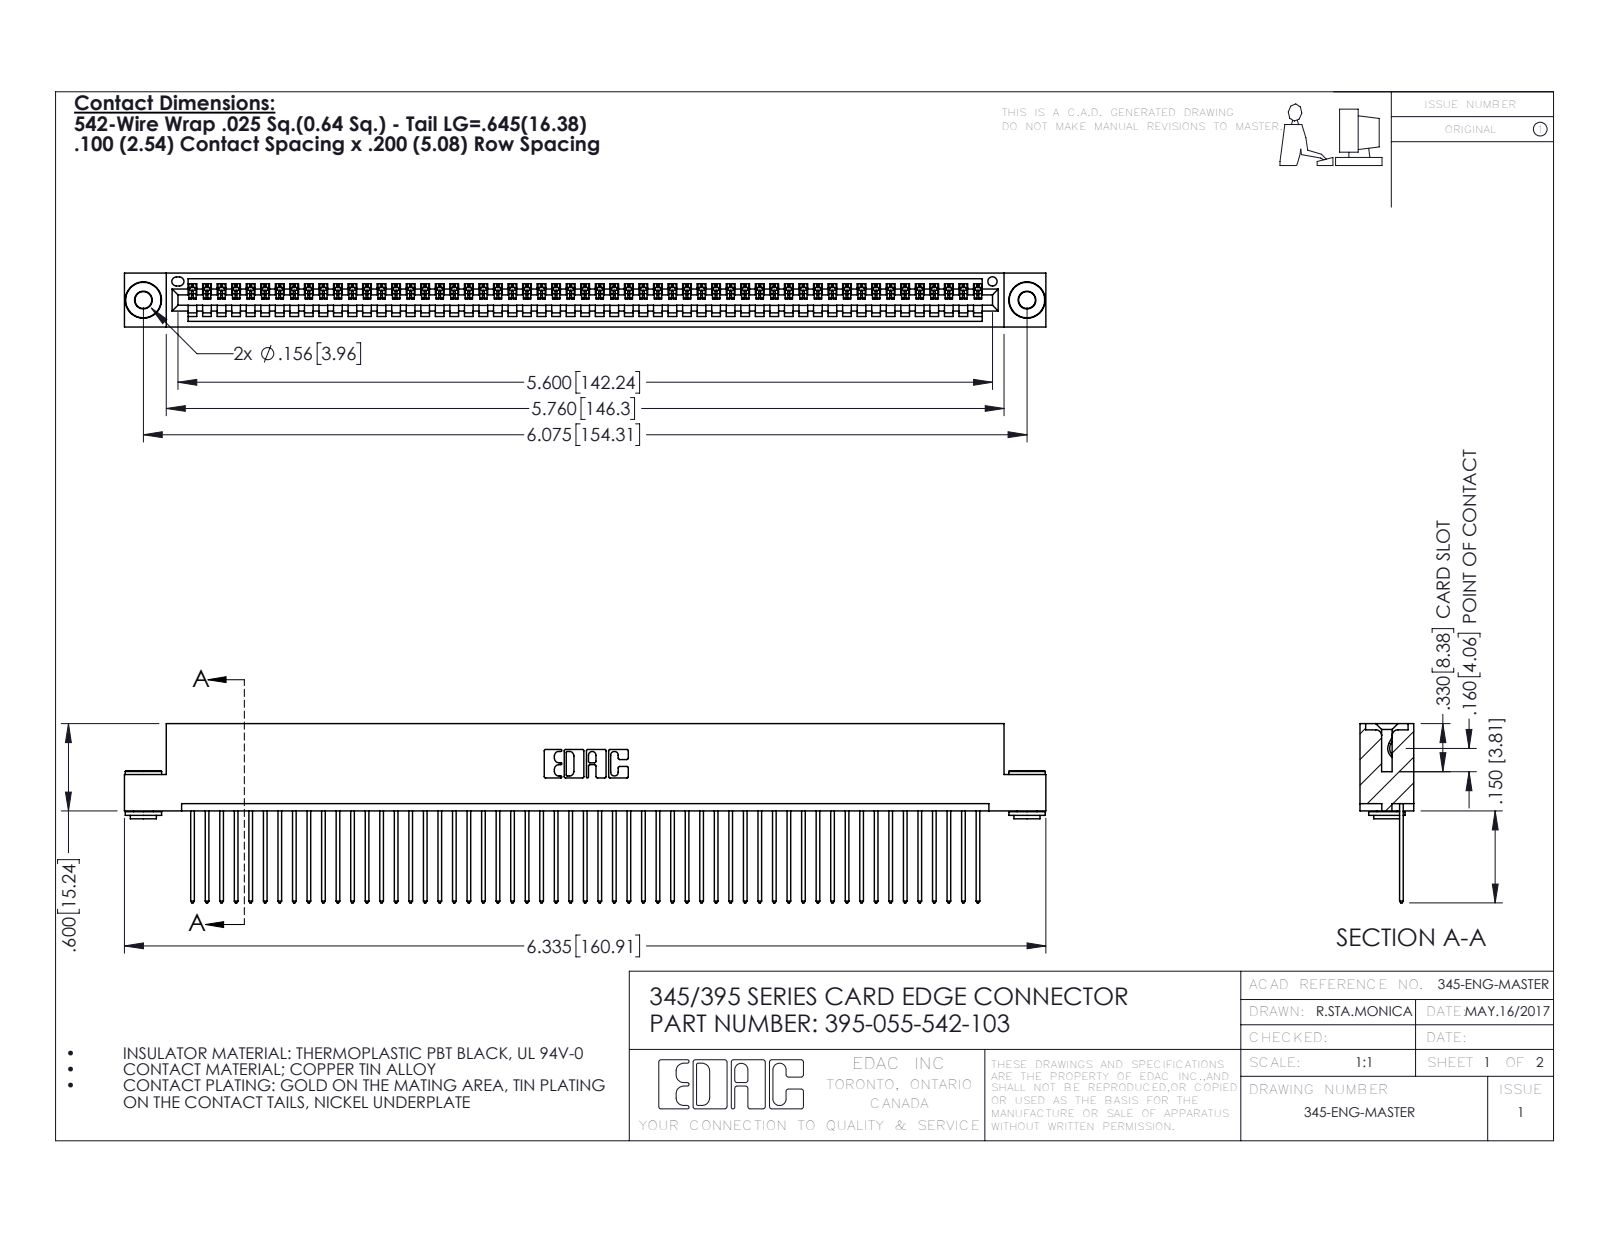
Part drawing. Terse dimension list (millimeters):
name: 345-292-001_345-293-142; 395-055-542-103; 345-250-002_345-250-002-102; 345 Part_Flush Mounting Lugs - 0.156 Dia-TH
written by: SolidWorks 2016 (CONFIG_CONTROL_DESIGN)
unit: mm
bodies: 58 solids, 3354 faces (2290 planar, 1056 cylindrical, 8 other)
size: 160.9 × 31.3 × 9.4
volume: 15 500 mm³; area: 21 810 mm²
holes: 2× ⌀2.9, 2× ⌀4, 1× ⌀1.6
bosses: 2× ⌀6.4, 2× ⌀4.6, 2× ⌀3.5
rounds: 110× R0.2, 110× R0.3, 22× R0.3, 6× R0.2, 6× R0.8, 3× R0.7, 2× R0.8, 2× R1
face distances: 1.8, 7.6, 0.6, 2.5, 6.9, 9.4, 5.1, 5.7, 3.8, 1.8
hole spacings: 6.9, 148.3, 154.3
